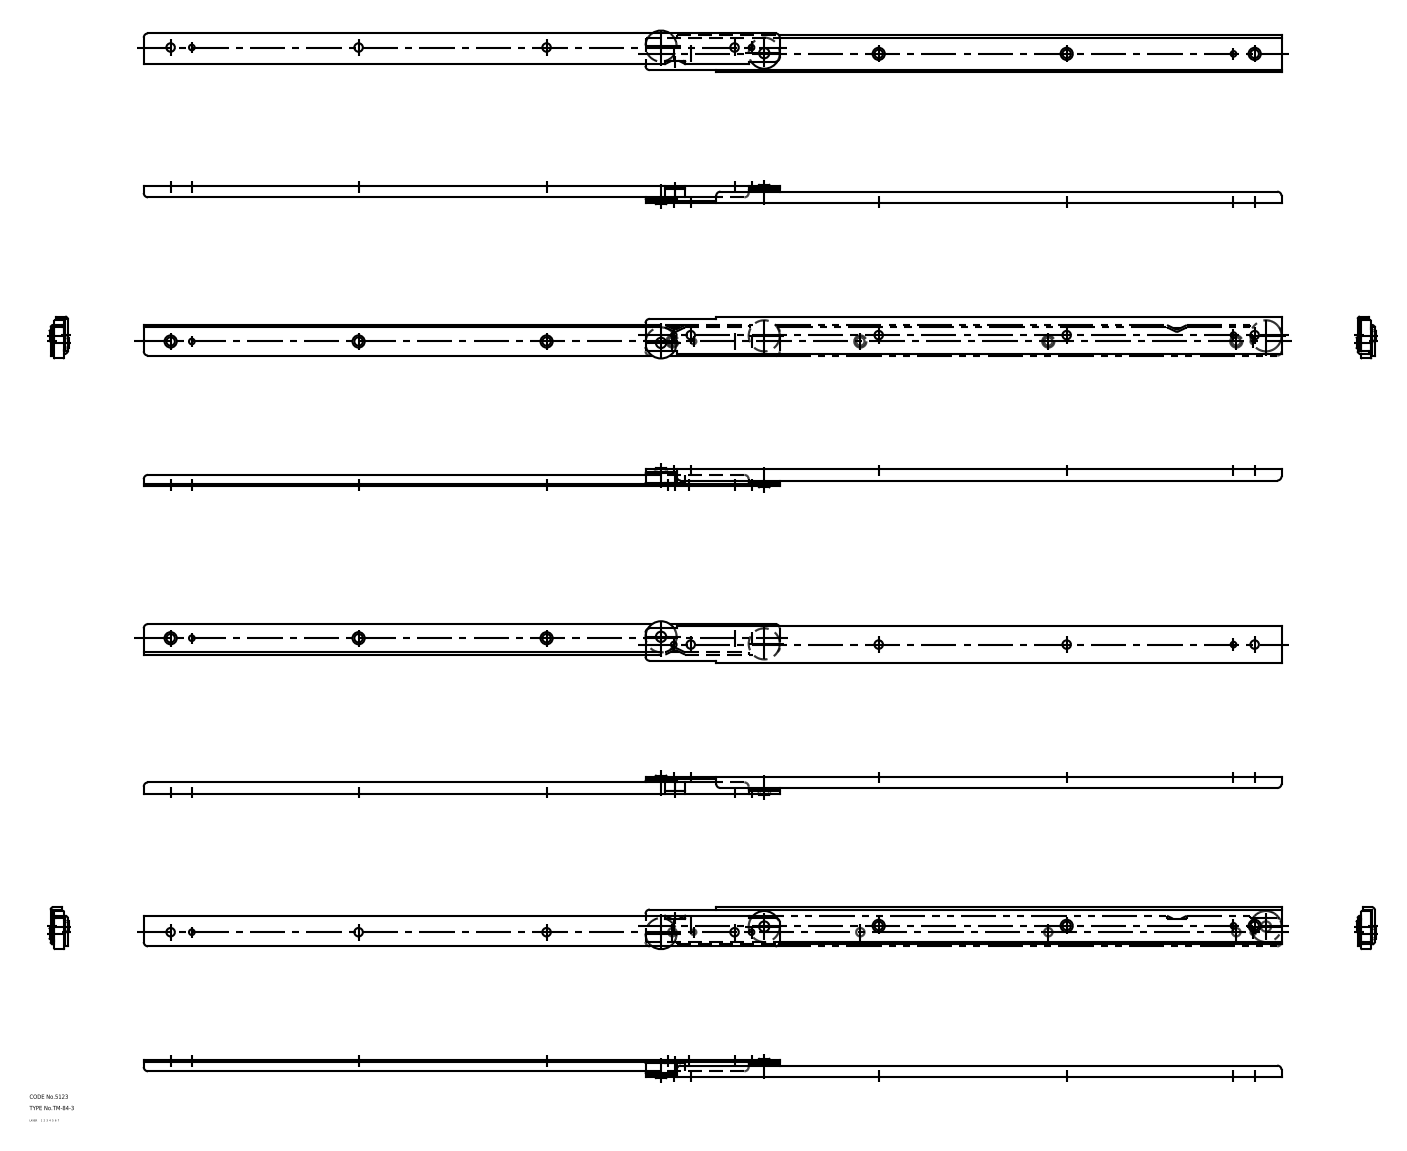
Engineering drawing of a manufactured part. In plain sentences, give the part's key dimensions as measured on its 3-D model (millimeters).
The part is named "roller; member_B; member_A; TM_84_3_6076_36". Its 3-D file was written by "CADfix (AUTOMOTIVE_DESIGN)". It is 4 solids with 115 faces: 0 planar, 0 cylindrical and 115 other. Overall it measures 805 by 29.6 by 13.4 millimeters. Its volume is 51 164 cubic millimeters and its surface area 63 191 square millimeters.
